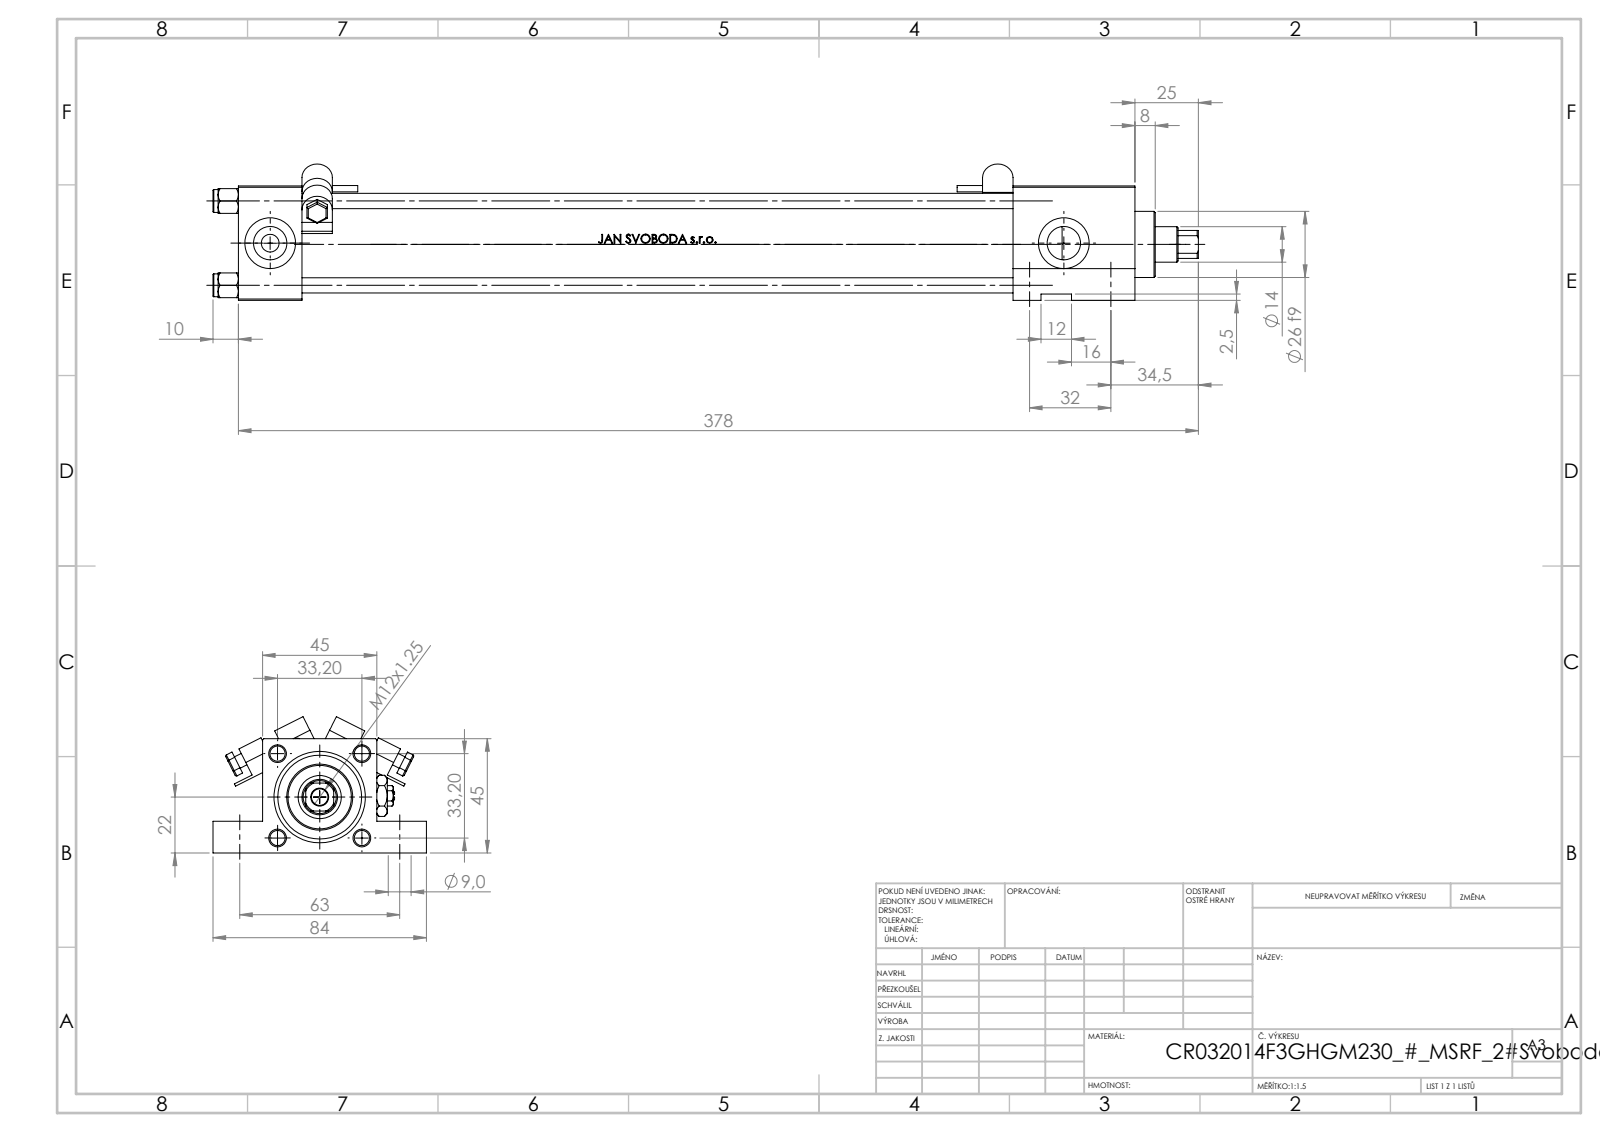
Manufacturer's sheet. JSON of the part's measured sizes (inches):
{"part_name": "V215CR_F_Body; NUT_M5_F; MSRF_MSRG1; V215_VC_A (+3 more)", "step_written_by": "SolidWorks 2019 (CONFIG_CONTROL_DESIGN)", "units": "inches", "bodies": {"solids": 15, "faces": 1262, "planar": 518, "cylindrical": 162, "other": 582}, "overall_size": [15.276, 3.307, 2.113], "volume_in3": 21.64, "surface_area_in2": 242.9, "round_holes": [[0.236, 4], [0.354, 4], [0.518, 3], [0.787, 3], [0.276, 2], [0.256, 1], [0.512, 1], [0.551, 1], [0.669, 1], [0.945, 1], [1.26, 1], [1.299, 1]], "round_bosses_or_shafts": [[0.354, 4], [0.197, 2], [0.098, 2], [1.496, 1], [1.024, 1]], "partial_cylinders_radius": [[0.02, 12], [0.236, 4], [0.256, 1]], "face_to_face_distances": [1.772, 0.984, 12.913, 1.89, 12.008, 11.024, 13.898, 1.28, 0.492, 0.394], "hole_center_spacings": [1.307, 0.911, 0.938, 1.26, 1.848, 2.48, 2.782, 0.276]}
